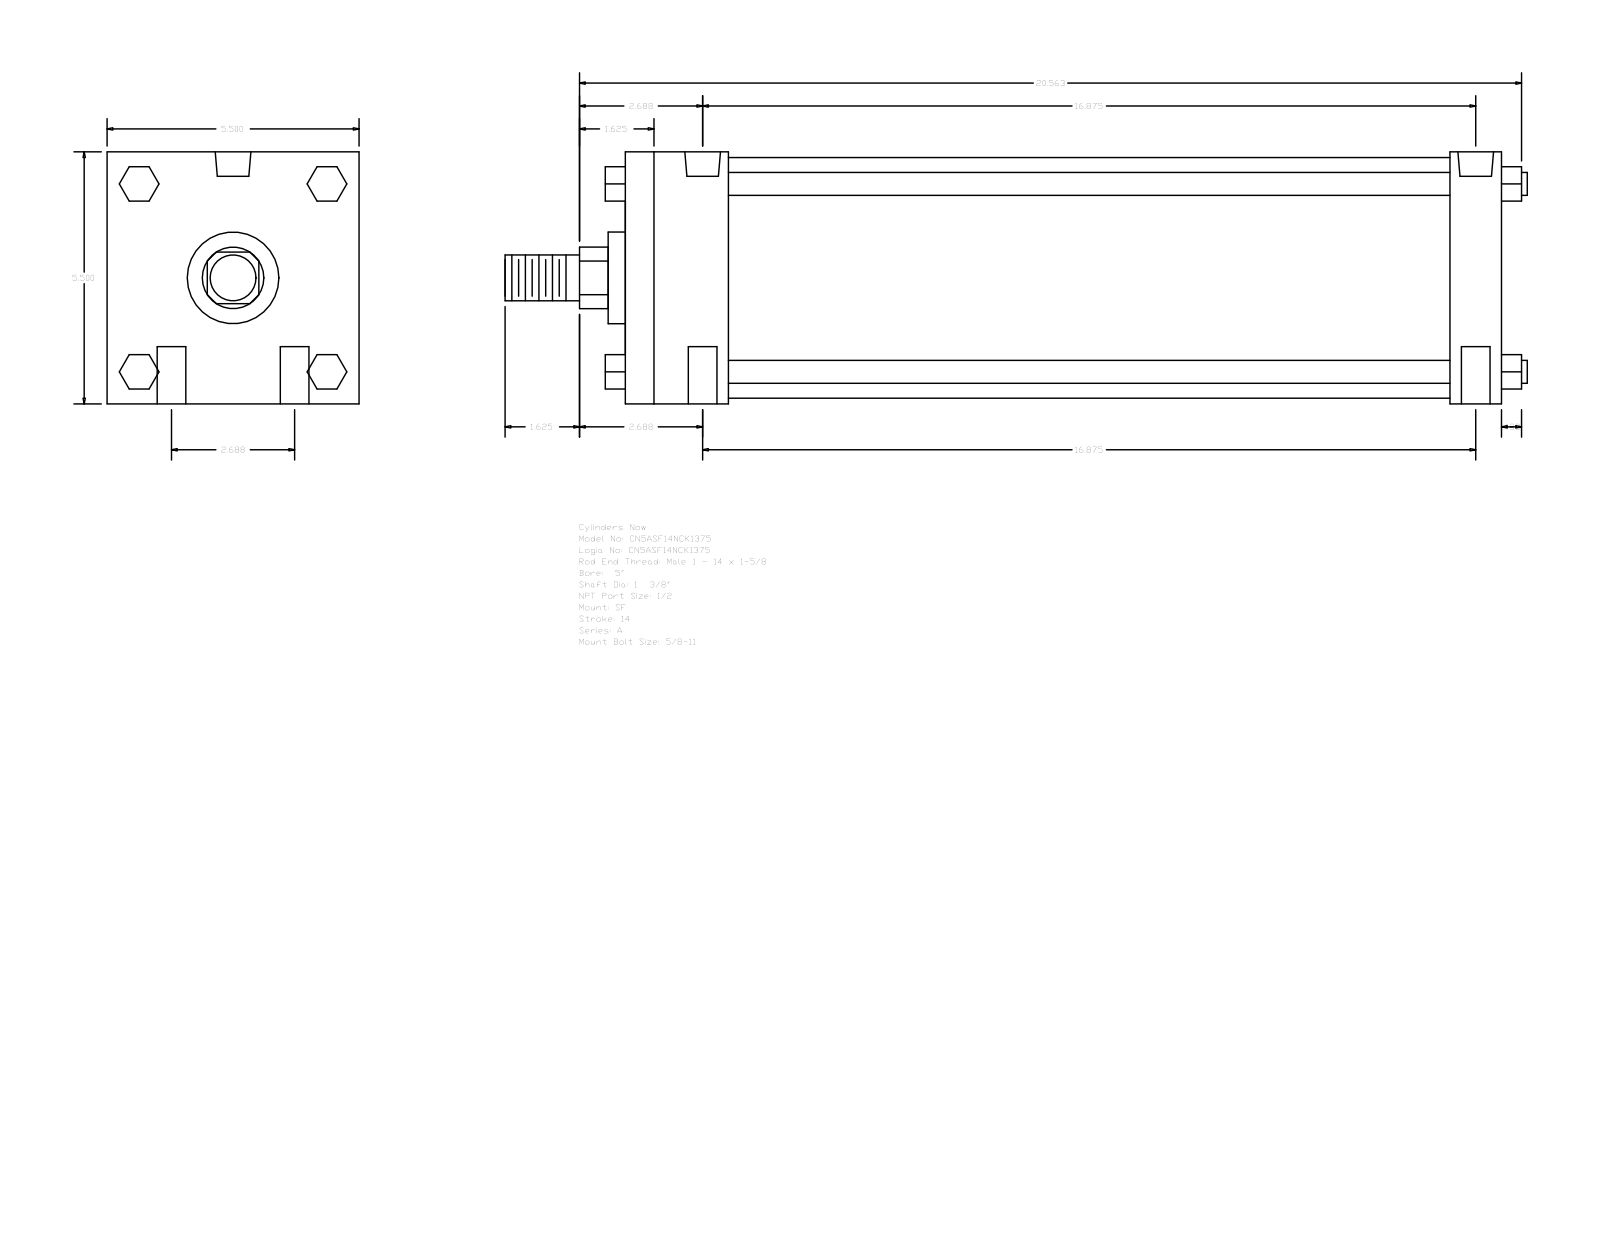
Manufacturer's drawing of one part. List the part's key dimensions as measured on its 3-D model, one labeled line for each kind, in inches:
Part name (STEP PRODUCT): A_SF__0500_1.375
STEP written by: GSSL Pune (CONFIG_CONTROL_DESIGN)
Units: inches
Bodies: 0 solids, 124 faces (94 planar, 30 cylindrical, 0 other)
Overall size (bounding box): 22.313 × 5.5 × 5.5
Round holes (diameter × count): ⌀0.625 ×4, ⌀0.344 ×2, ⌀0.778 ×2
Round bosses / shafts (diameter × count): ⌀0.5 ×4, ⌀5.25 ×1, ⌀2 ×1, ⌀1.375 ×1, ⌀1 ×1
Partial cylindrical surfaces — rounded edges, fillets, slot ends (radius × count): R0.672 ×1
Main face-to-face distances: 5.5, 19.125, 2.25, 1.125, 18, 15.75, 16.875, 0.75, 2.05, 3.55
Hole centre spacings: 1.344, 16.929, 16.875, 2.687, 17.088, 16.687
